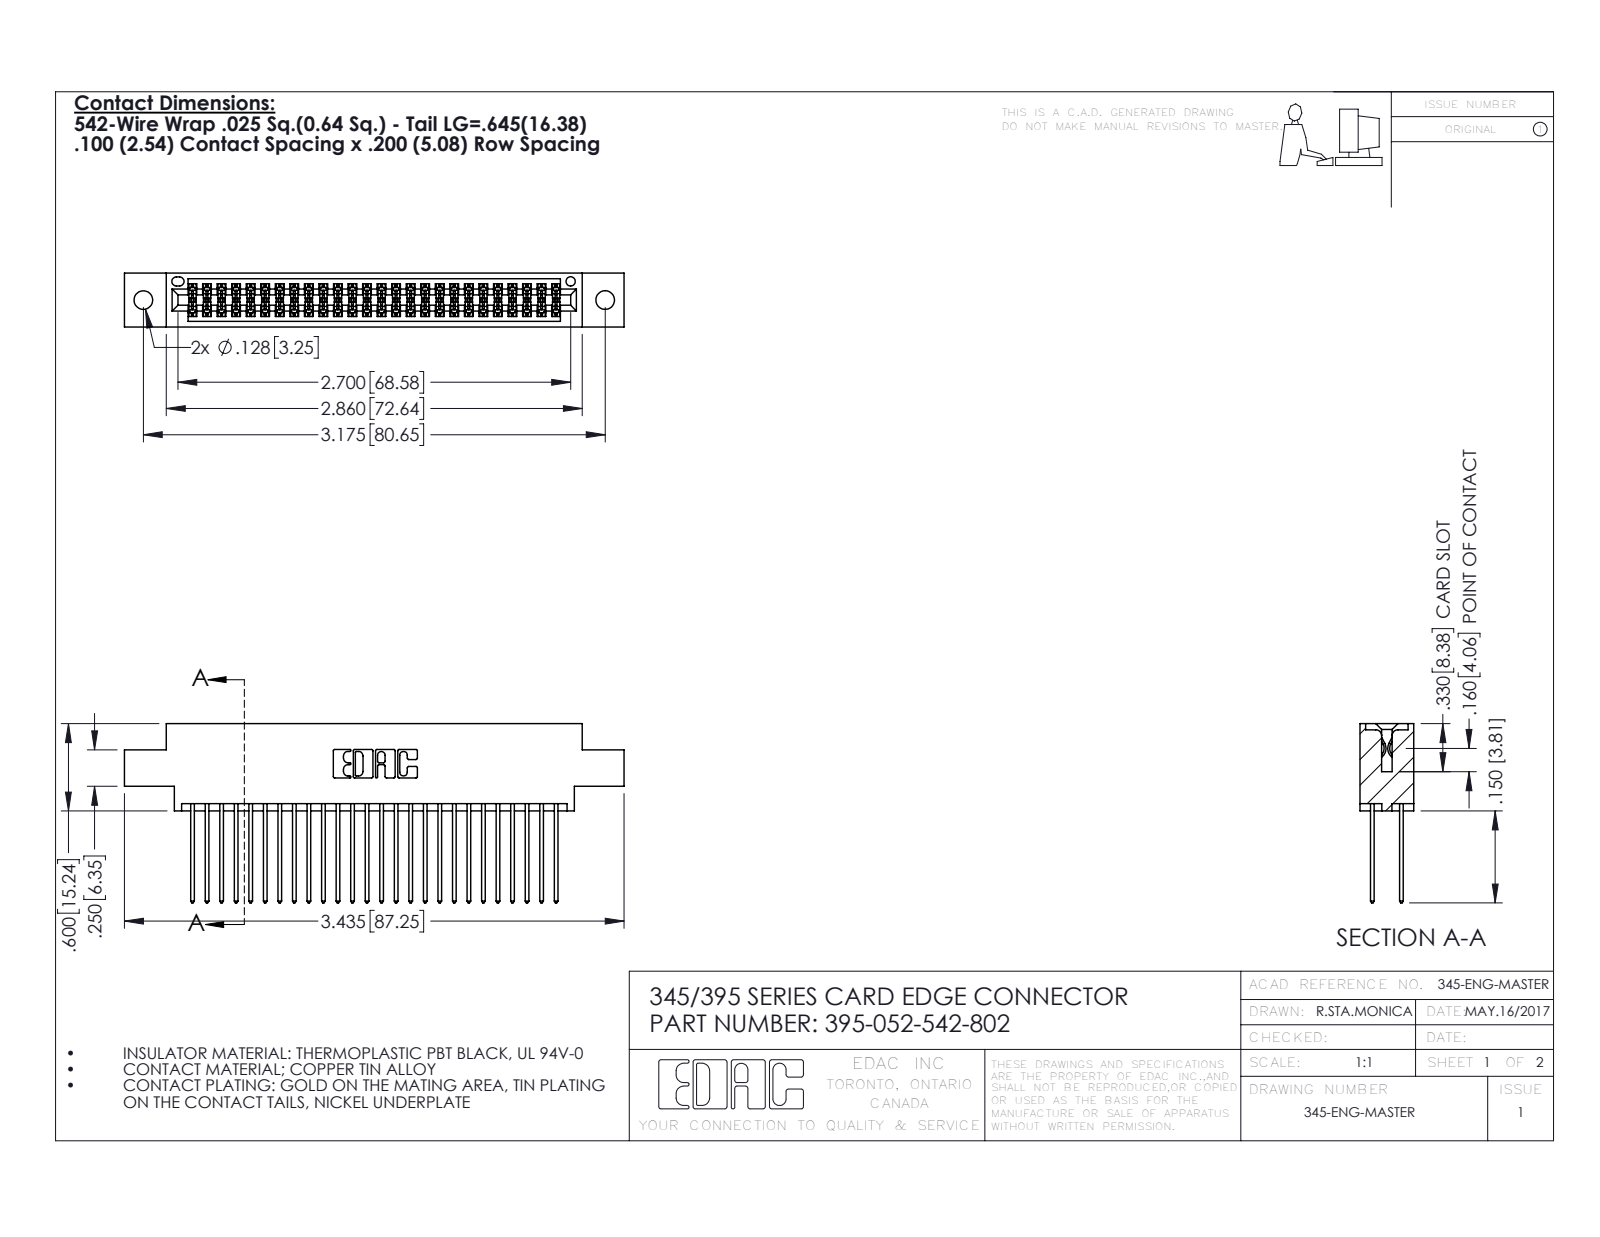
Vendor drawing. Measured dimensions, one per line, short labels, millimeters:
name: 395-052-542-802; 345 Part_0.170 Offset - 0.128 Dia; 345-292-001_345-293-142
written by: SolidWorks 2016 (CONFIG_CONTROL_DESIGN)
unit: mm
bodies: 53 solids, 2730 faces (1800 planar, 930 cylindrical, 0 other)
size: 87.2 × 31.3 × 9.4
volume: 8 420 mm³; area: 13 140 mm²
holes: 2× ⌀3.3, 1× ⌀1.6
rounds: 78× R0.2, 52× R0.3, 22× R0.3, 6× R0.2, 6× R0.8, 3× R0.7, 2× R0.4, 2× R0.5
face distances: 7.6, 1.8, 5.1, 2.5, 6.9, 0.6, 9.4, 5.7, 4.4, 3.8
hole spacings: 6.9, 74.7, 80.6
